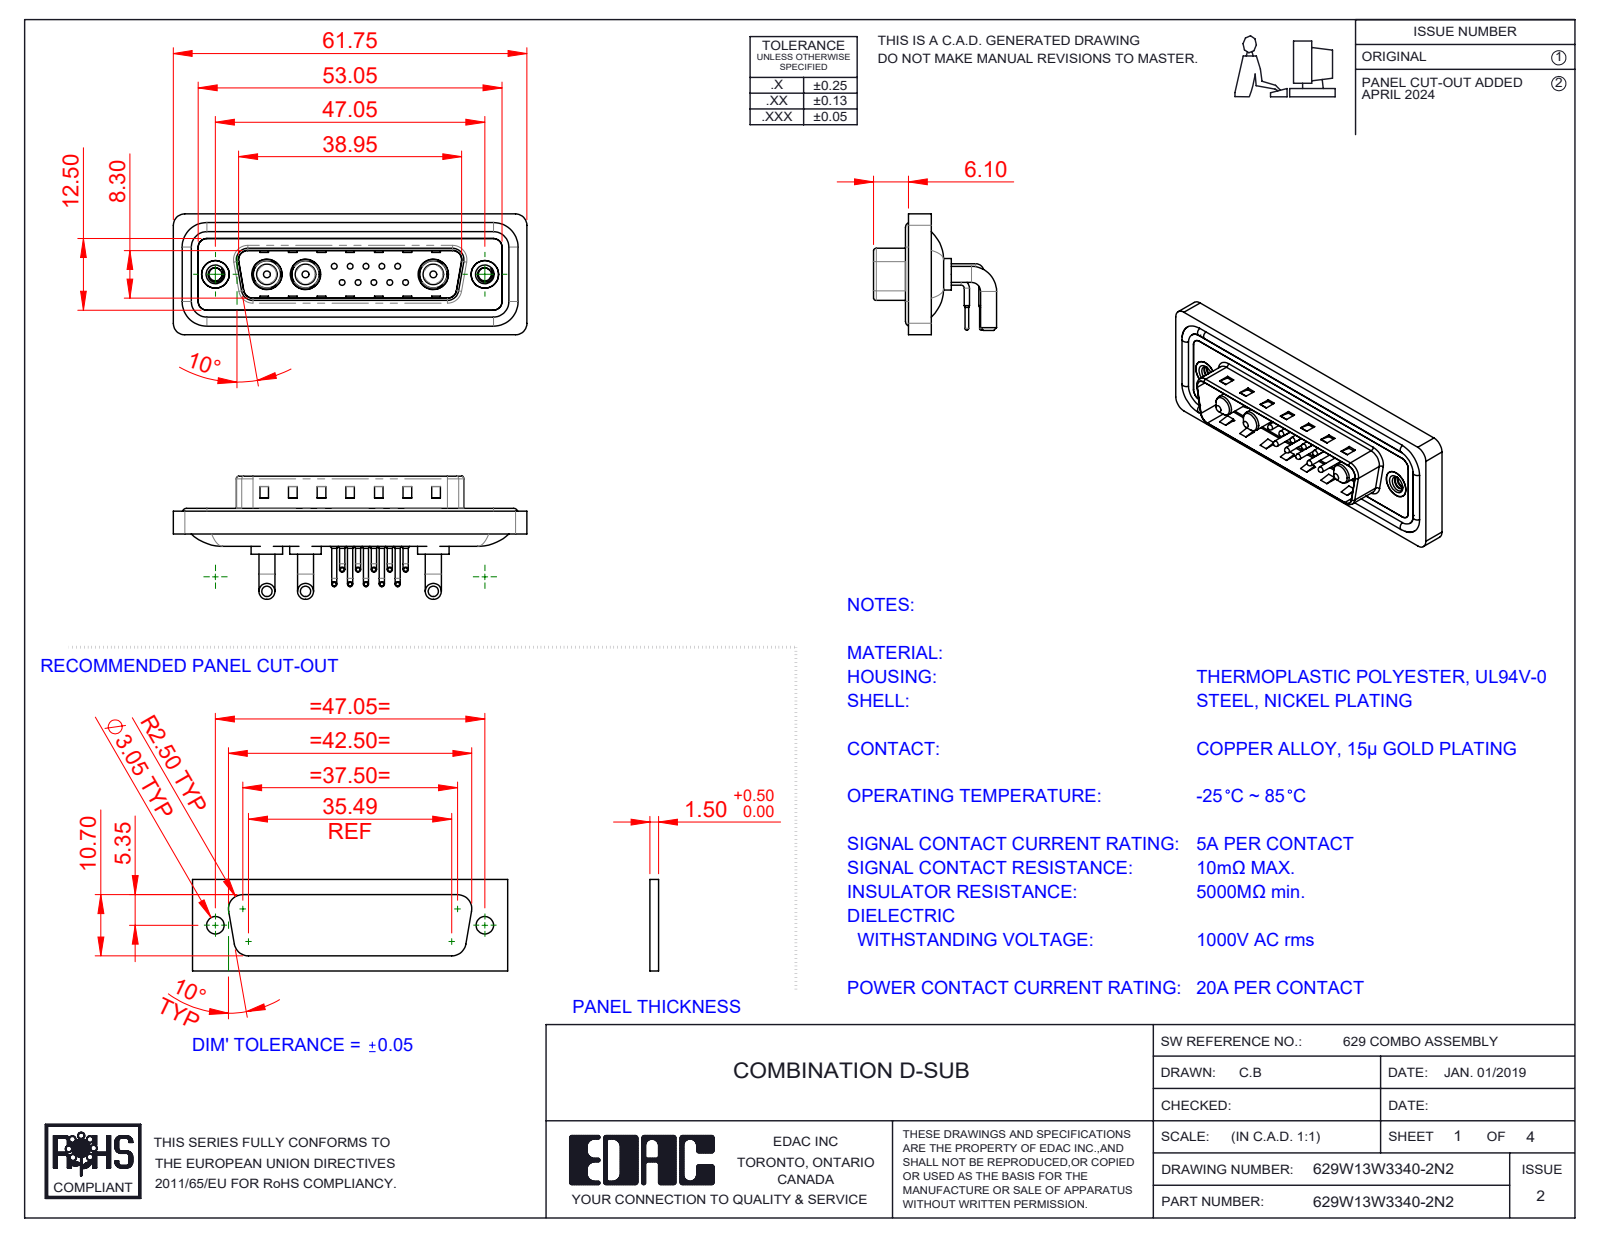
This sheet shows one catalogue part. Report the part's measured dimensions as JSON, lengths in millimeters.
{"part_name": "Power Pin_20A RA; 629Combo Shell Front_25 Contacts; 629Combo Contact Row 1; 629Combo Housing_13W3 (+5 more)", "step_written_by": "SolidWorks 2023 (CONFIG_CONTROL_DESIGN)", "units": "millimeters", "bodies": {"solids": 23, "faces": 1712, "planar": 879, "cylindrical": 611, "other": 222}, "overall_size": [61.75, 21.5, 21.1], "volume_mm3": 7621, "surface_area_mm2": 12497, "round_holes": [[0.75, 10], [1.6, 10], [2, 10], [4.85, 3], [5.3, 3], [2.26, 2], [4, 2], [4.8, 2], [5, 2]], "round_bosses_or_shafts": [[0.9, 20], [1.5, 10], [1, 10], [0.65, 10], [2.8, 6], [1.6, 4], [5.5, 3], [5.2, 3]], "partial_cylinders_radius": [[1.5, 18], [2, 18], [1.01, 10], [0.5, 8], [1.6, 8], [0.25, 4], [0.6, 4], [0.65, 4]], "face_to_face_distances": [0.4, 2.9, 0.8, 4.1, 1.1, 2.1, 1.6, 4.5, 1.5, 2.5], "hole_center_spacings": [3.16, 2.77, 5.04, 5.54, 7.49, 5.03, 8.31, 10.11]}
